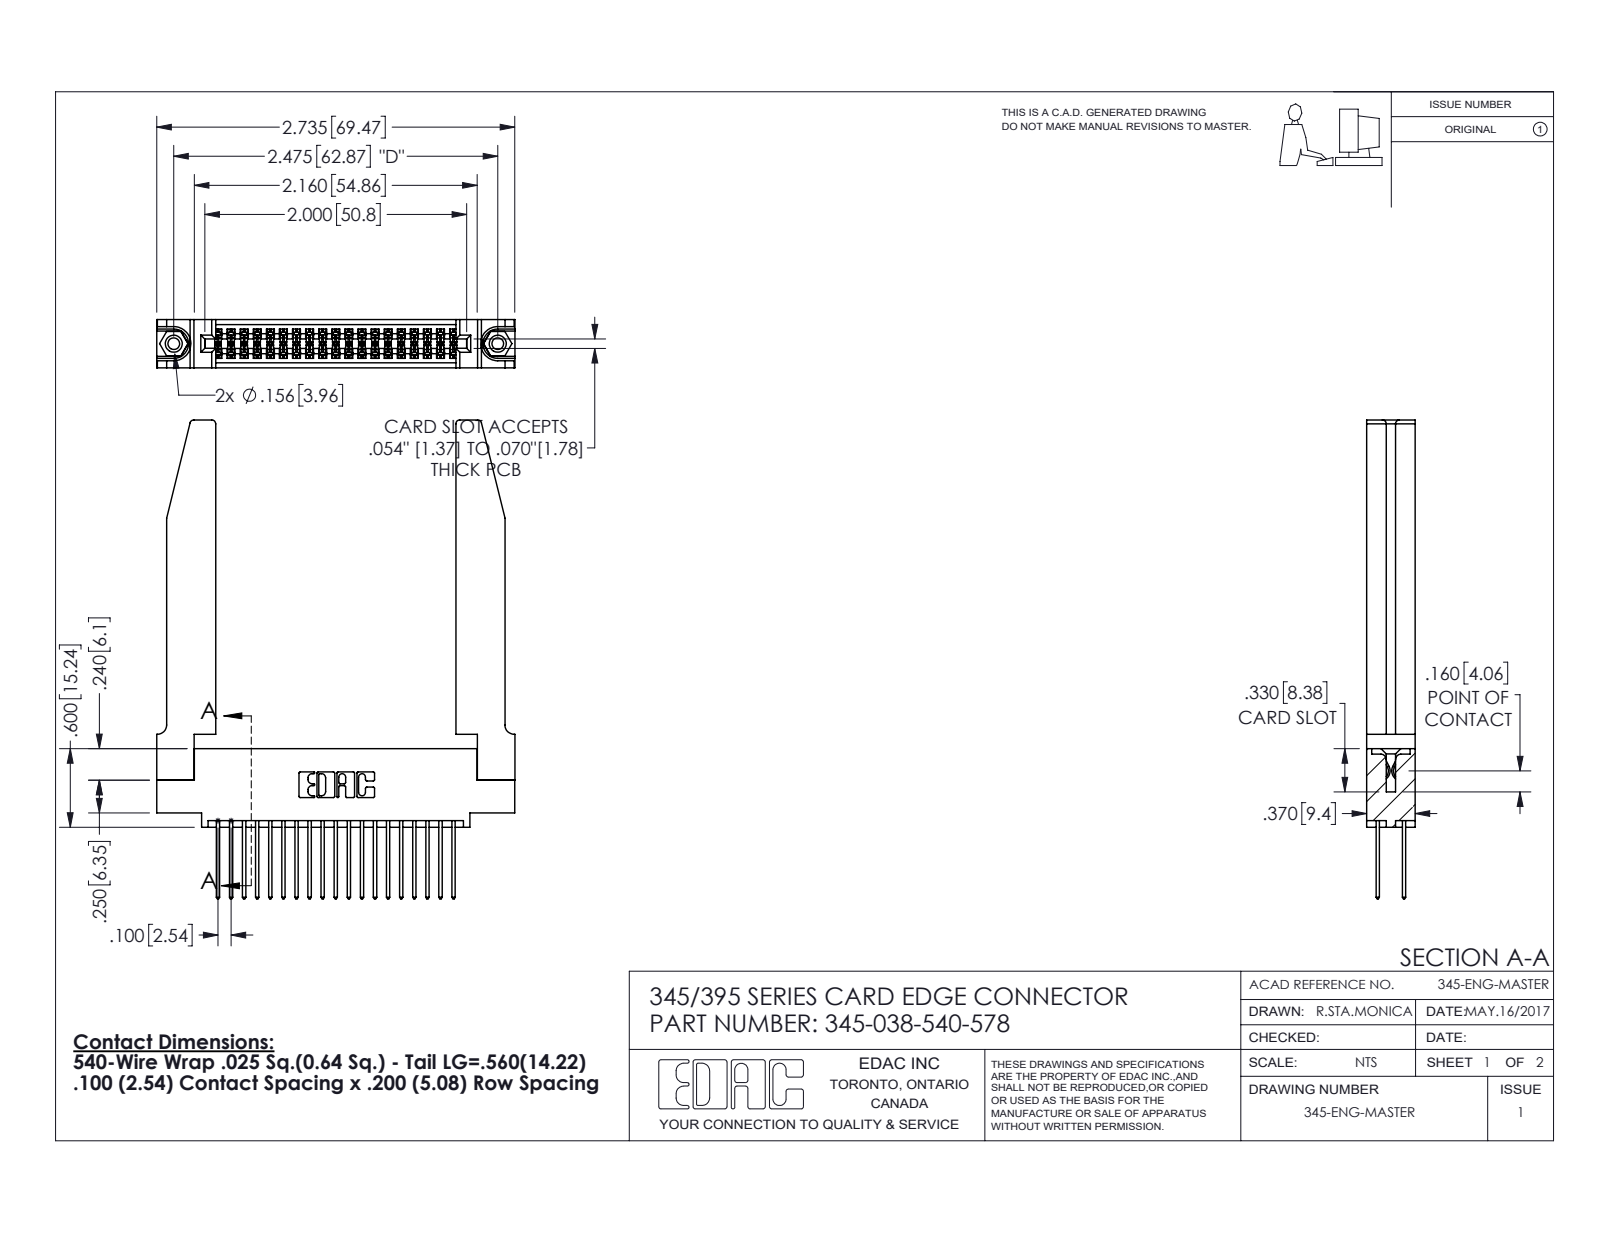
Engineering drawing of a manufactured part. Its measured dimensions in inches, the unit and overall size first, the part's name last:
Units: inches
Overall size (bounding box): 3.657 × 2.736 × 0.37
Round holes (diameter × count): ⌀0.089 ×2, ⌀0.125 ×2, ⌀0.156 ×2, ⌀0.064 ×1
Round bosses / shafts (diameter × count): ⌀0.155 ×2
Partial cylindrical surfaces — rounded edges, fillets, slot ends (radius × count): R0.006 ×57, R0.01 ×38, R0.01 ×22, R0.03 ×8, R0.007 ×6, R0.031 ×6, R0.026 ×3, R0.014 ×2
Main face-to-face distances: 0.37, 0.072, 0.298, 0.2, 0.098, 0.272, 0.025, 0.225, 0.148, 0.15
Hole centre spacings: 0.27, 2.241, 2.475
Volume: 0.877 in³ · Surface area: 26.23 in²
Bodies: 43 solids, 2264 faces (1480 planar, 732 cylindrical, 52 other)
Part name (STEP PRODUCT): 345 Part_0.110 Offset - 0.156 Dia-TH; 345-292-001_345-293-140; 345-220-078_345-220-078; 345-250-001_345-250-001-102 (+1 more)
STEP written by: SolidWorks 2016 (CONFIG_CONTROL_DESIGN)
